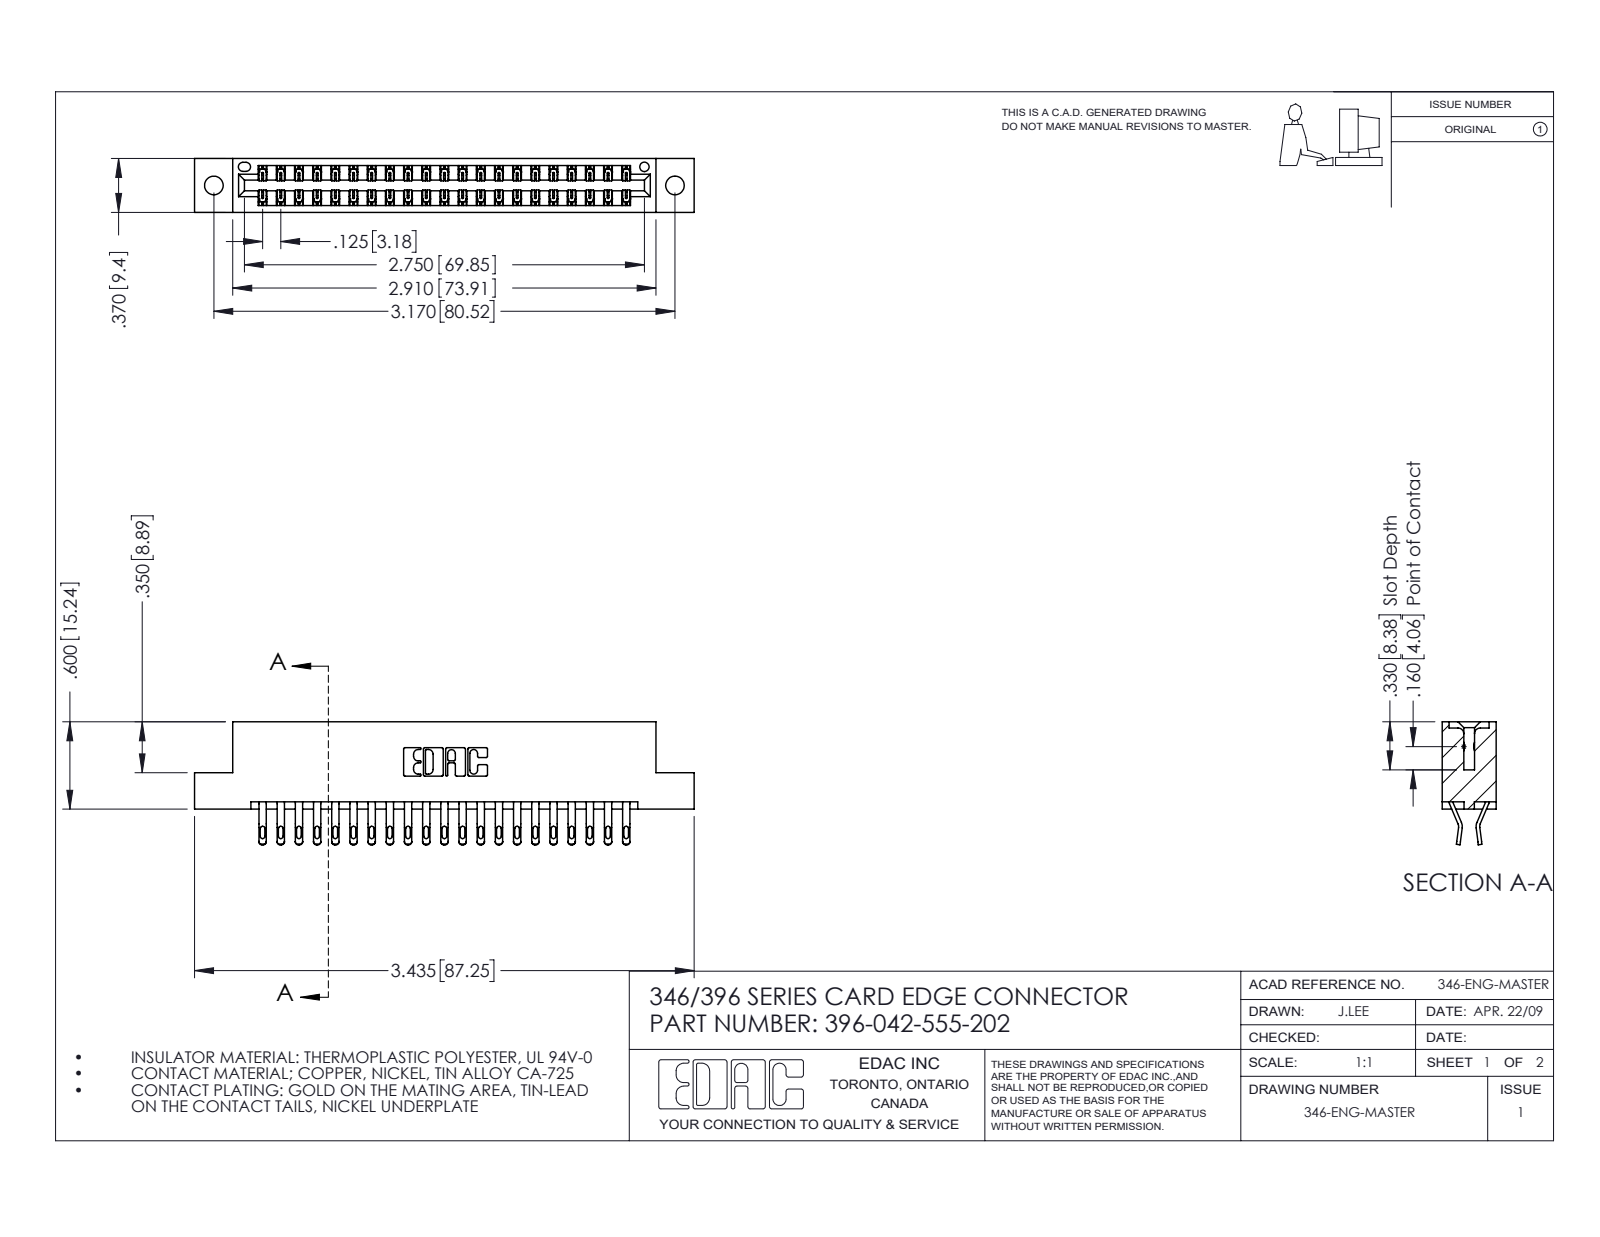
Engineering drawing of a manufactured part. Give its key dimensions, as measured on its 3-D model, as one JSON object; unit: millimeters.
{"part_name": "396-042-555-202; 345-292-001_555 Tail; 346 Part_Flush Mounting Lugs - 0.128 Dia", "step_written_by": "SolidWorks 2016 (CONFIG_CONTROL_DESIGN)", "units": "millimeters", "bodies": {"solids": 43, "faces": 2558, "planar": 1462, "cylindrical": 1096, "other": 0}, "overall_size": [87.2, 21.5, 9.4], "volume_mm3": 8420, "surface_area_mm2": 11420, "round_holes": [[3.3, 2], [1.6, 1]], "partial_cylinders_radius": [[0.4, 84], [0.5, 84], [0.2, 63], [0.3, 22], [0.2, 6], [0.8, 6], [0.7, 3], [0.3, 2]], "face_to_face_distances": [1.2, 8.2, 6.4, 9.4, 0.6, 1.8, 7.6, 7, 3.8, 5.6], "hole_center_spacings": [6.2, 75.3, 80.5]}
